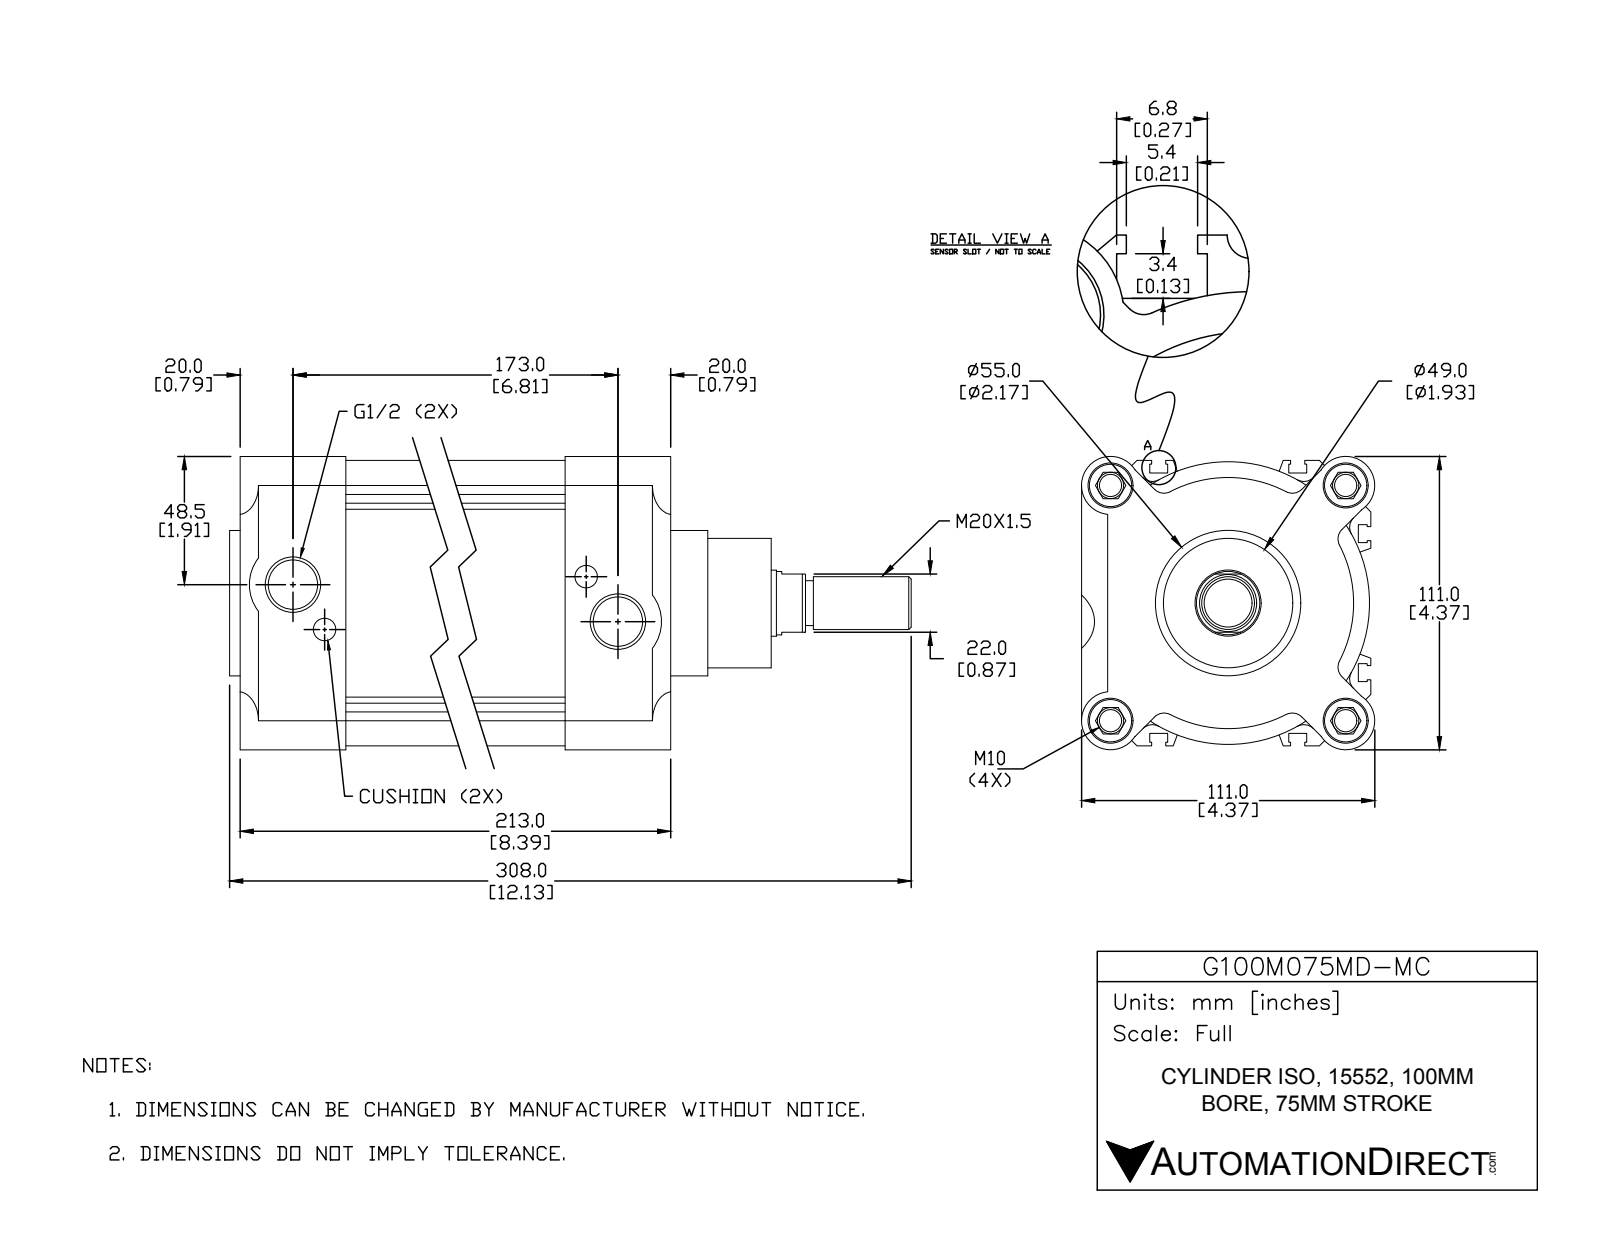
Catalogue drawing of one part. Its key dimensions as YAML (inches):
part_name: "G100M075MD-MC; 100-75-120.5-B; 10012175-R; 100121-HR (+1 more)"
step_written_by: "SolidWorks 2015 (CONFIG_CONTROL_DESIGN)"
units: inches
bodies: {solids: 4, faces: 462, planar: 248, cylindrical: 162, other: 52}
overall_size: [12.126, 4.37, 4.37]
volume: 111.3
surface_area: 449
round_holes:
  - {diameter: 0.33, count: 4}
  - {diameter: 0.669, count: 4}
  - {diameter: 0.335, count: 2}
  - {diameter: 0.734, count: 2}
  - {diameter: 0.984, count: 1}
round_bosses_or_shafts:
  - {diameter: 0.63, count: 4}
  - {diameter: 3.937, count: 1}
  - {diameter: 2.165, count: 1}
  - {diameter: 1.929, count: 1}
  - {diameter: 0.945, count: 1}
  - {diameter: 0.787, count: 1}
  - {diameter: 0.669, count: 1}
partial_cylinders:
  - {radius: 0.197, count: 12}
  - {radius: 0.004, count: 6}
  - {radius: 0.374, count: 4}
  - {radius: 0.433, count: 4}
  - {radius: 0.65, count: 2}
  - {radius: 1.87, count: 1}
  - {radius: 2.087, count: 1}
  - {radius: 2.106, count: 1}
face_to_face_distances: [6.417, 0.394, 4.843, 1.575, 1.969, 6.811, 1.496, 3.465, 4.449, 2.953]
hole_center_spacings: [2.478, 3.504, 0.819, 4.956, 6.34, 5.919, 6.833]
